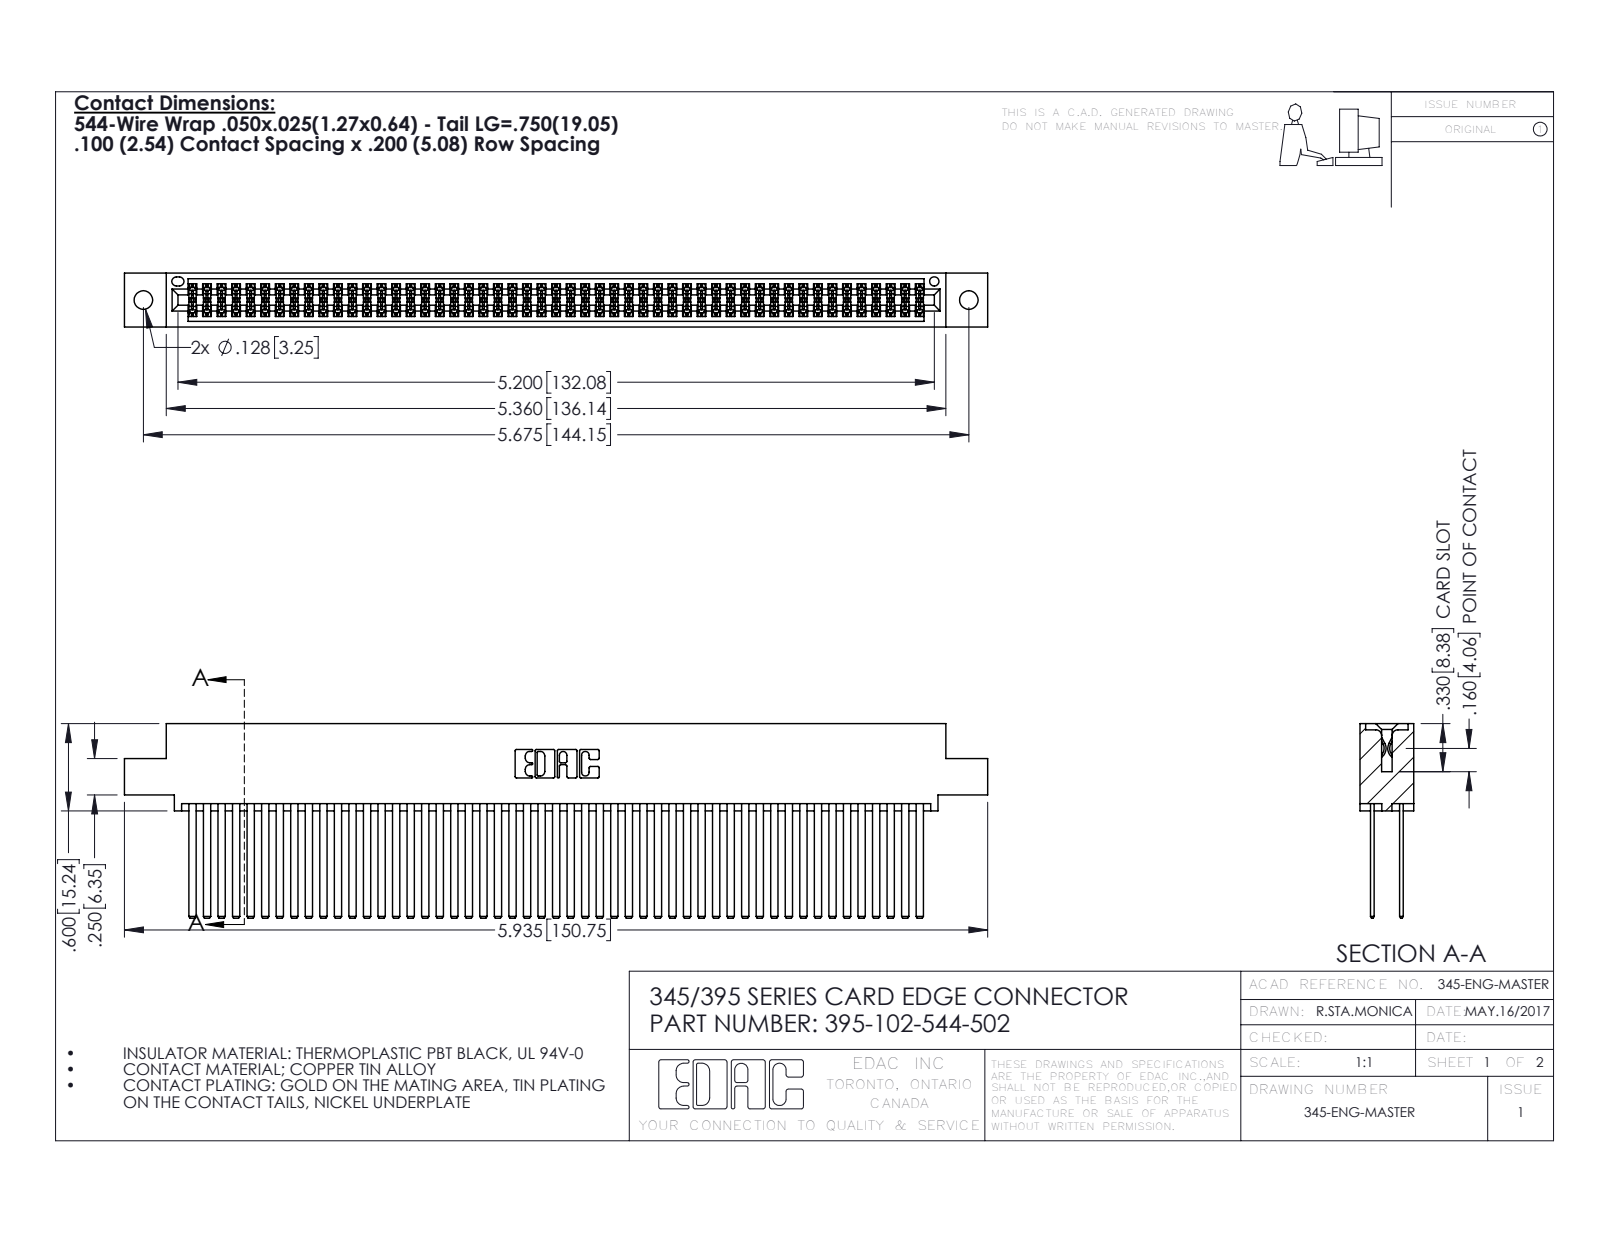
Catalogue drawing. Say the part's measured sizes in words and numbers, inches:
The part is named "345 Part_0.110 Offset - 0.128 Dia; 395-102-544-502; 345-292-001_345-293-144". Its 3-D file was written by "SolidWorks 2016 (CONFIG_CONTROL_DESIGN)". It is 103 solids with 4618 faces: 3042 planar, 1576 cylindrical and 0 other. Overall it measures 5.935 by 1.337 by 0.37 inches. Its volume is 0.979 cubic inches and its surface area 43.25 square inches. Round holes: 2 of diameter 0.128, 1 of diameter 0.064. Partial cylindrical surfaces (rounded edges, fillets, slot ends): 153 of radius 0.006, 22 of radius 0.01, 6 of radius 0.007, 6 of radius 0.031, 3 of radius 0.026, 2 of radius 0.014, 2 of radius 0.019, 2 of radius 0.022. The main face-to-face distances are 0.2, 0.025, 0.298, 0.072, 0.098, 0.272, 0.225, 0.175, 0.37, 0.05. The hole center spacings are 0.27, 5.439, 5.675.
